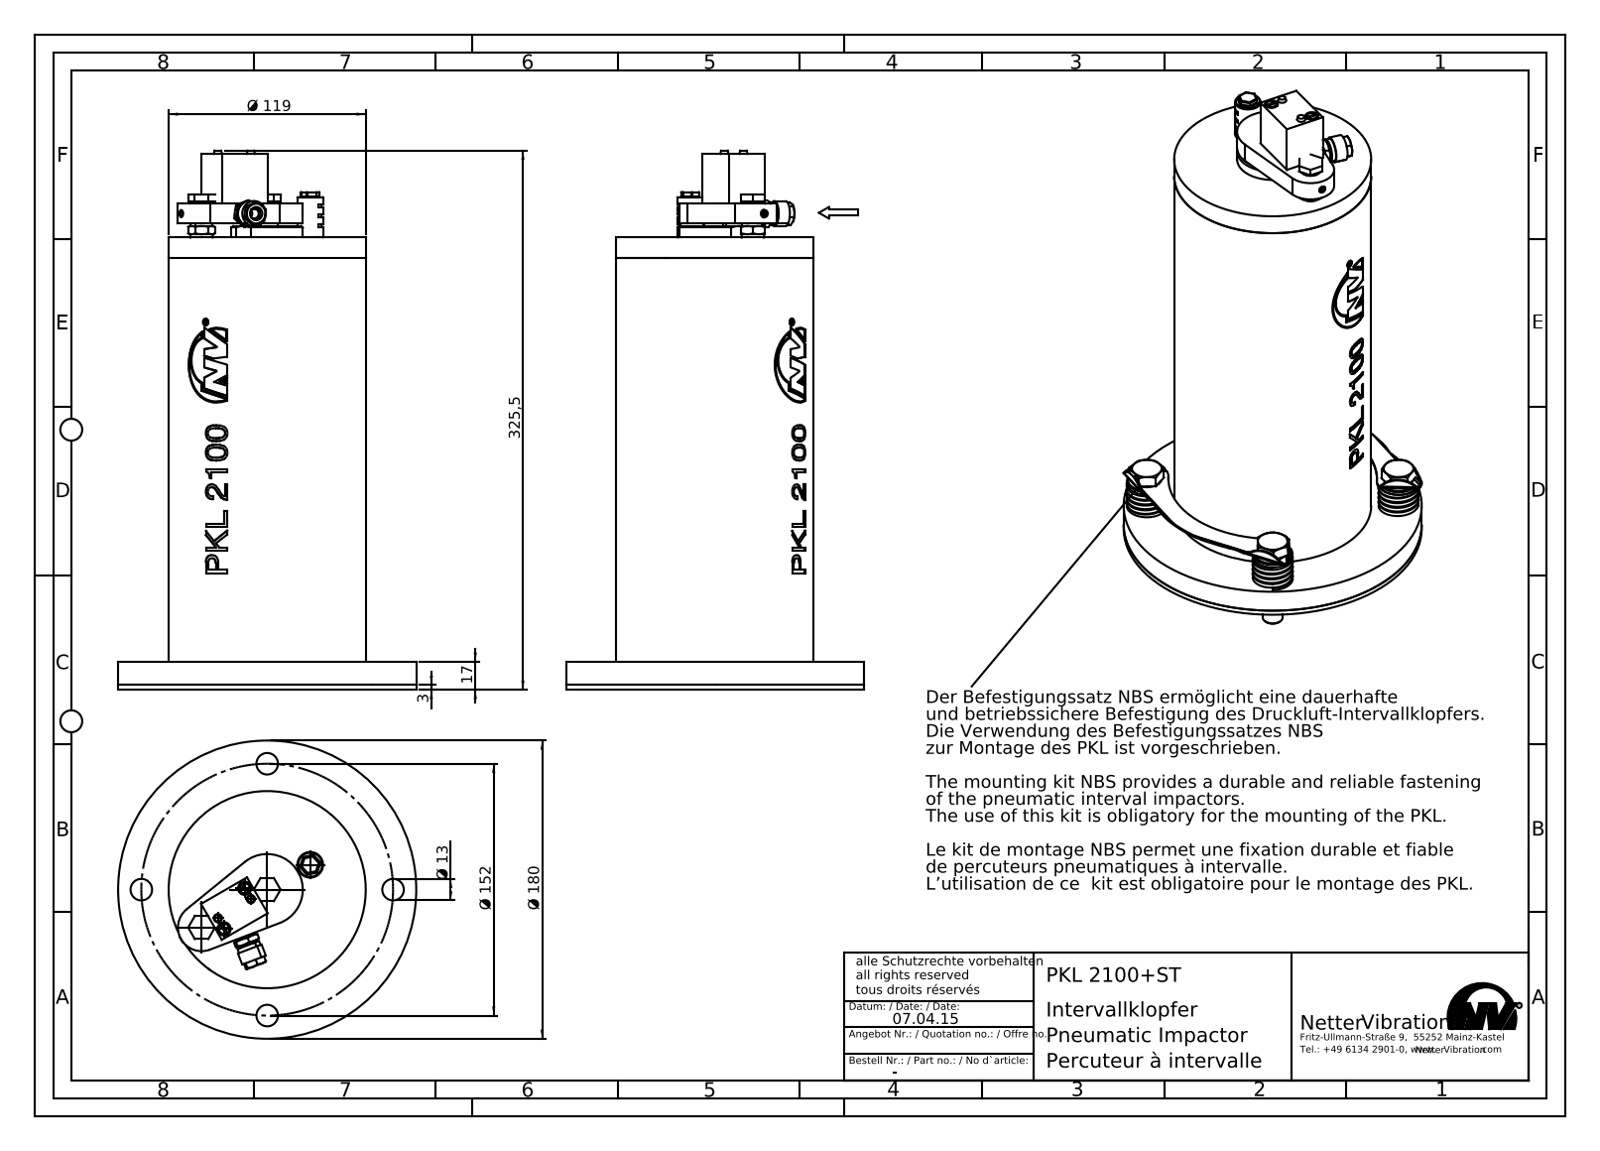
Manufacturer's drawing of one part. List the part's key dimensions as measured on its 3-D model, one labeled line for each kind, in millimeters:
Part name (STEP PRODUCT): PKL 2100+ST
STEP written by: SolidWorks 2015 (AUTOMOTIVE_DESIGN)
Units: millimetres
Bodies: 23 solids, 881 faces (337 planar, 237 cylindrical, 307 other)
Overall size (bounding box): 338.5 × 180 × 180
Volume: 3 655 000 mm³ · Surface area: 340 988 mm²
Round holes (diameter × count): ⌀8.57 ×4, ⌀12.5 ×4, ⌀13 ×4, ⌀13.4 ×4, ⌀17 ×4, ⌀3.5 ×3, ⌀4 ×3, ⌀8 ×3, ⌀3.3 ×2, ⌀4.2 ×2, ⌀4.5 ×2, ⌀5 ×2
Round bosses / shafts (diameter × count): ⌀24.3 ×4, ⌀24 ×4, ⌀18 ×4, ⌀12 ×4, ⌀9.73 ×3, ⌀13 ×2, ⌀9.6 ×2, ⌀8.94 ×2
Partial cylindrical surfaces — rounded edges, fillets, slot ends (radius × count): R0.5 ×18, R15 ×12, R1 ×8, R2 ×8, R12 ×8, R24 ×4, R7 ×1, R14.25 ×1
Main face-to-face distances: 3, 14, 17, 257.5, 12.5, 260.5, 243.5, 273, 270, 256
Hole centre spacings: 76, 107.48, 1, 7.51, 11.38, 13.63, 24.18, 34.37
